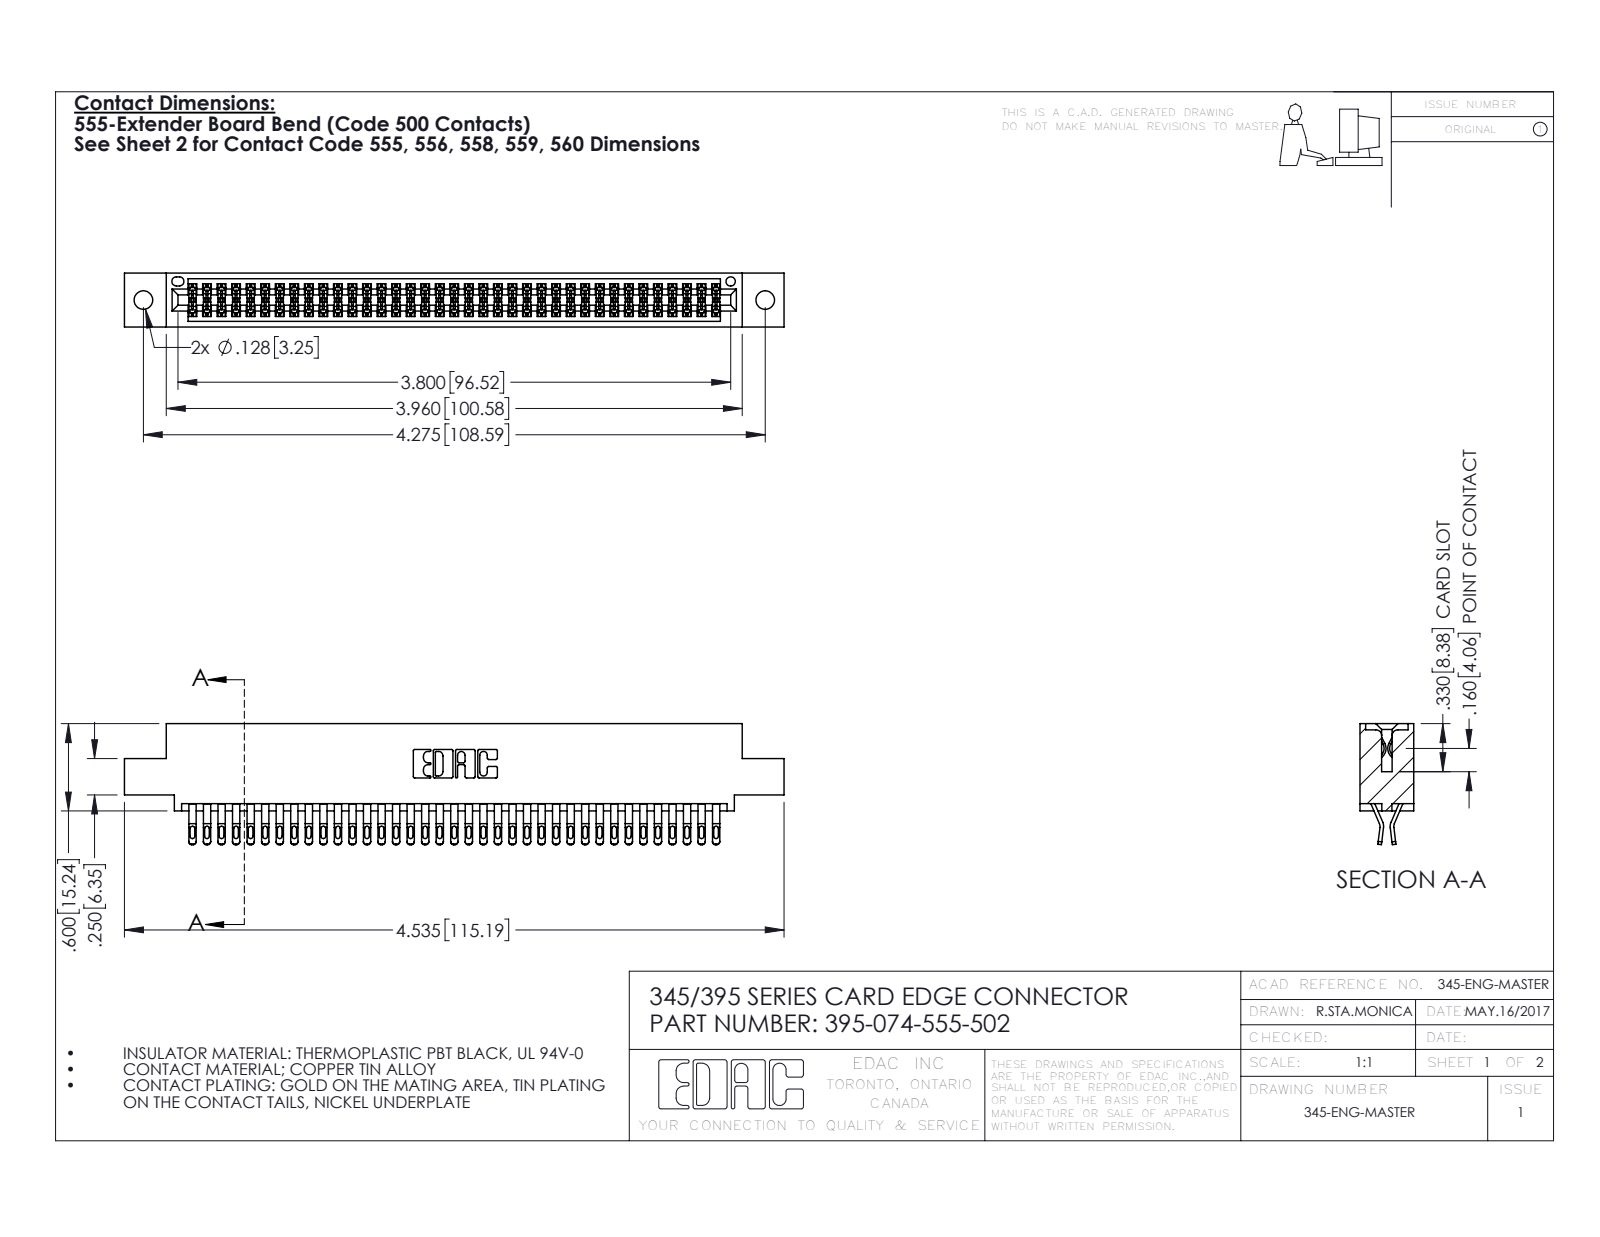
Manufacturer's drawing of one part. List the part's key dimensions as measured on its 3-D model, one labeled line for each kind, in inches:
Part name (STEP PRODUCT): 345-292-001_555 Tail; 395-074-555-502; 345 Part_0.110 Offset - 0.128 Dia
STEP written by: SolidWorks 2016 (CONFIG_CONTROL_DESIGN)
Units: inches
Bodies: 75 solids, 4274 faces (2378 planar, 1896 cylindrical, 0 other)
Overall size (bounding box): 4.535 × 0.832 × 0.37
Volume: 0.686 in³ · Surface area: 26.5 in²
Round holes (diameter × count): ⌀0.128 ×2, ⌀0.064 ×1
Partial cylindrical surfaces — rounded edges, fillets, slot ends (radius × count): R0.016 ×185, R0.02 ×148, R0.006 ×111, R0.01 ×22, R0.007 ×6, R0.031 ×6, R0.026 ×3, R0.01 ×2
Main face-to-face distances: 0.298, 0.072, 0.025, 0.37, 0.2, 0.098, 0.272, 0.225, 0.175, 0.149
Hole centre spacings: 0.27, 4.039, 4.275
